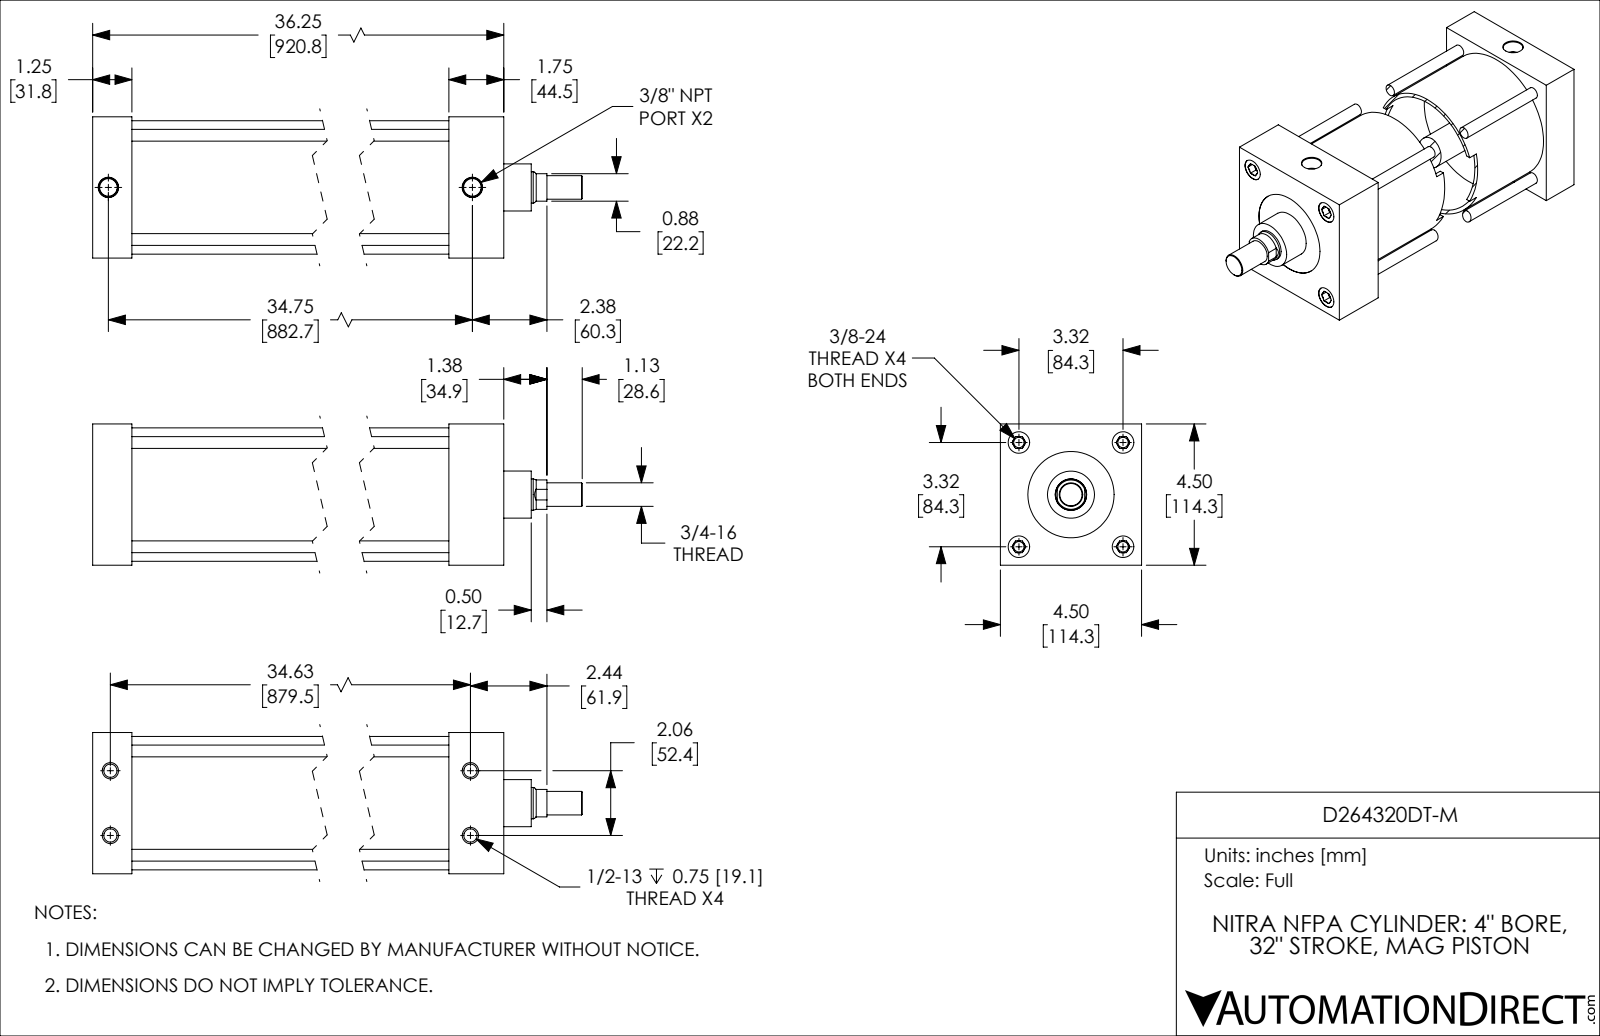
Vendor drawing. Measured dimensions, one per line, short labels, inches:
name: D264320DT-M_BODY; D264320DT-M_PISTON_KK1; D264320DT-M
written by: SolidWorks 2019 (CONFIG_CONTROL_DESIGN)
unit: in
bodies: 2 solids, 198 faces (58 planar, 62 cylindrical, 78 other)
size: 38.75 × 4.5 × 4.5
volume: 170.1 in³; area: 1 334 in²
holes: 4× ⌀0.332, 4× ⌀0.422, 4× ⌀0.687, 2× ⌀0.562, 1× ⌀1.001, 1× ⌀2.75, 1× ⌀4.001
bosses: 4× ⌀0.375, 1× ⌀4.251, 1× ⌀3.999, 1× ⌀1.5, 1× ⌀0.999, 1× ⌀0.75
rounds: 1× R0.469
face distances: 1.25, 4.5, 34.5, 33.25, 36.25, 35, 1.75, 2.5, 32, 33.75
hole spacings: 2.347, 3.32, 34.703, 1.033, 4.695, 34.625, 34.686, 1.034
